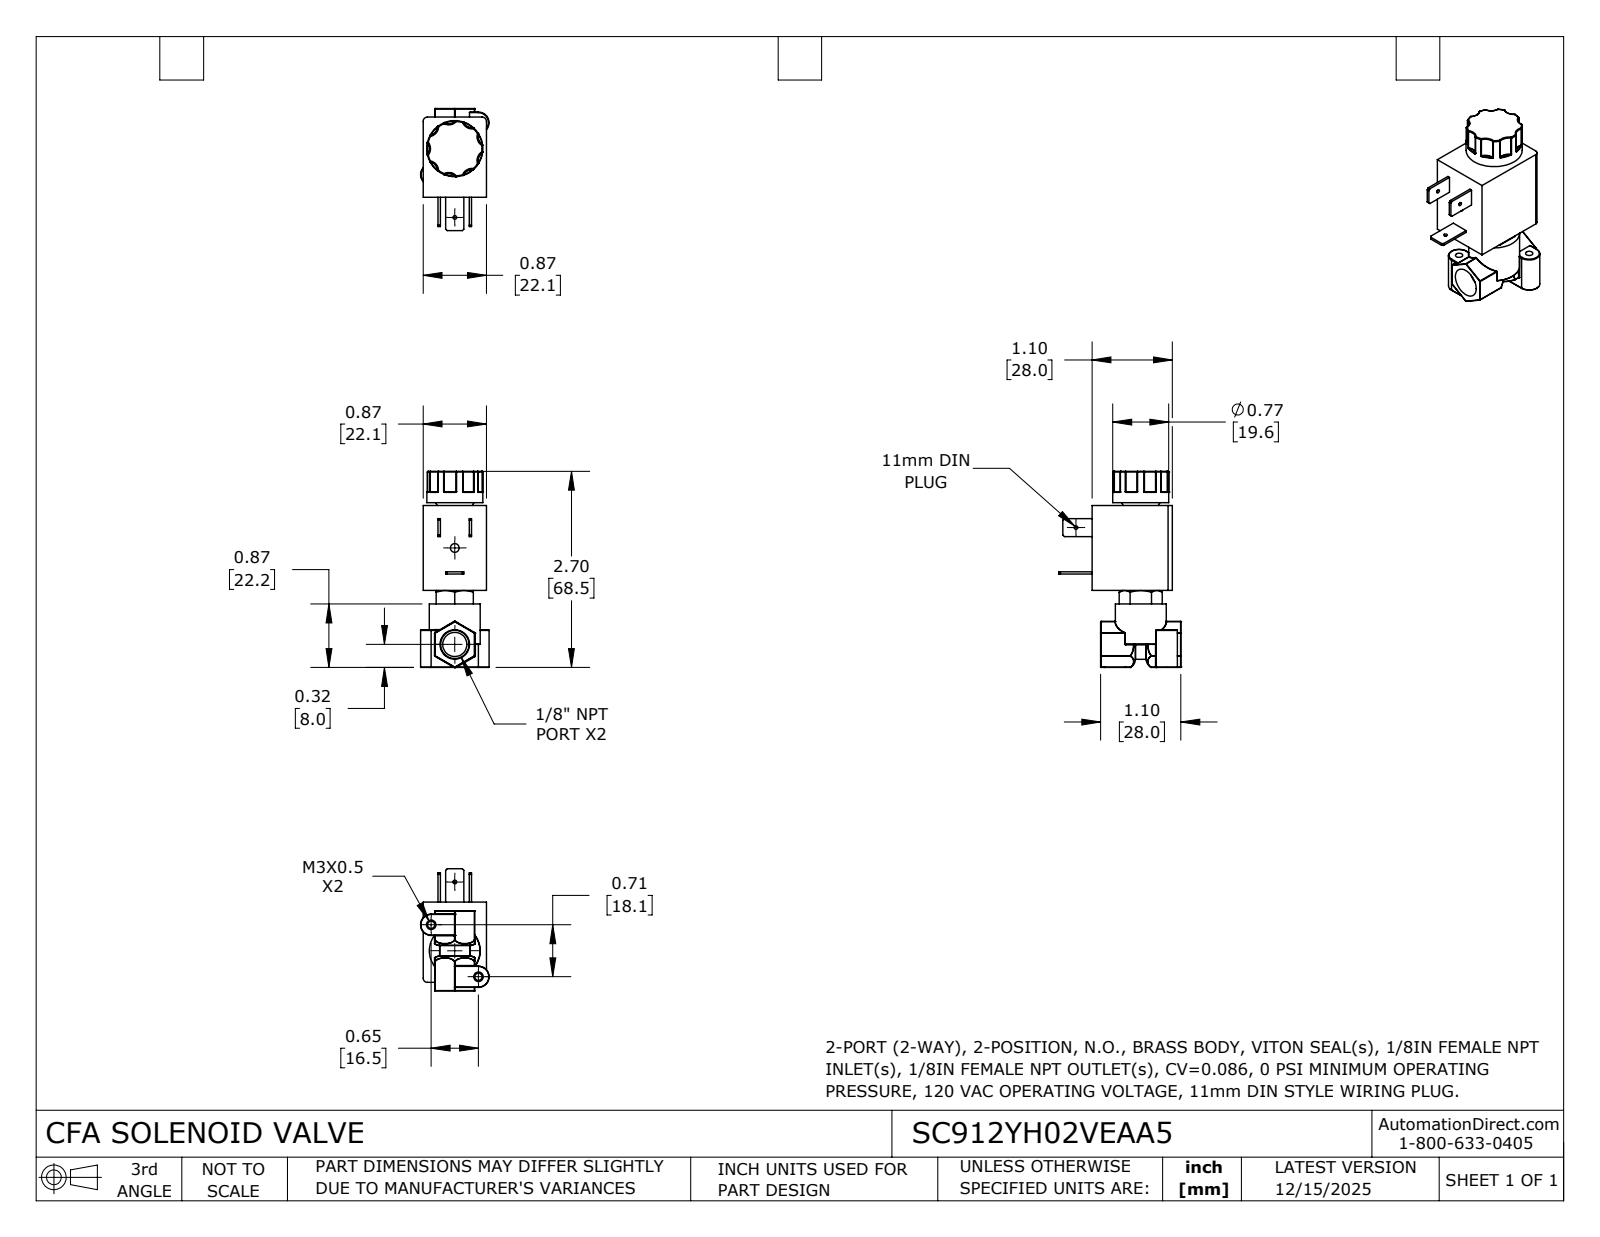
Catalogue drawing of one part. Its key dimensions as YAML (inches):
part_name: "SC912YH02VEAA5"
step_written_by: "SolidWorks 2024 (CONFIG_CONTROL_DESIGN)"
units: inches
bodies: {solids: 1, faces: 397, planar: 76, cylindrical: 110, other: 211}
overall_size: [2.695, 1.678, 0.942]
volume: 1.739
surface_area: 14.05
round_holes:
  - {diameter: 0.05, count: 2}
  - {diameter: 0.1, count: 2}
  - {diameter: 0.12, count: 1}
  - {diameter: 0.332, count: 1}
round_bosses_or_shafts:
  - {diameter: 0.77, count: 1}
  - {diameter: 0.7, count: 1}
partial_cylinders:
  - {radius: 0.004, count: 29}
  - {radius: 0.01, count: 18}
  - {radius: 0.008, count: 12}
  - {radius: 0.133, count: 7}
  - {radius: 0.017, count: 2}
  - {radius: 0.06, count: 2}
  - {radius: 0.132, count: 2}
  - {radius: 0.146, count: 2}
face_to_face_distances: [0.87, 1.104, 1.167, 1.637, 0.47, 0.548, 0.031, 0.161, 0.709, 1.207]
hole_center_spacings: [0.672, 0.965, 1.326, 1.342]
